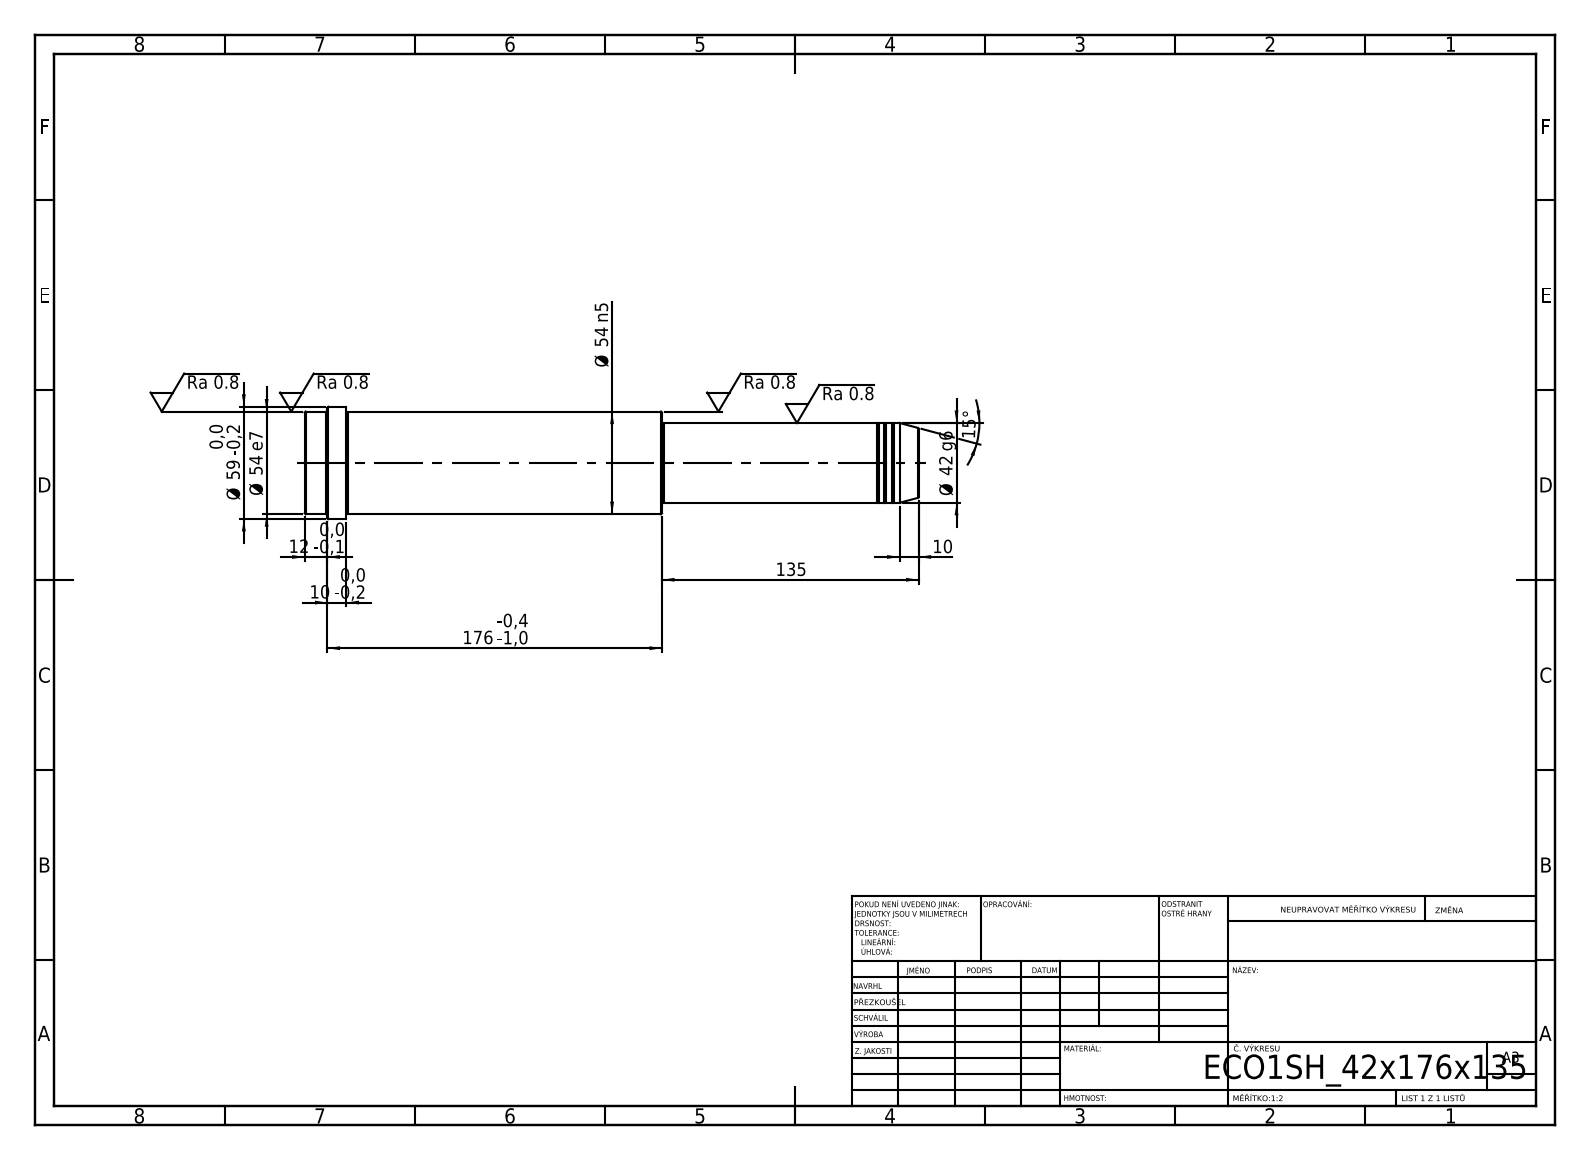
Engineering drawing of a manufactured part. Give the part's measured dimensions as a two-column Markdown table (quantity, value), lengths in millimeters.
| quantity | value |
| --- | --- |
| STEP written by | SolidWorks 2019 (CONFIG_CONTROL_DESIGN) |
| units | millimeters |
| bodies | 1 solid, 52 faces (6 planar, 16 cylindrical, 30 other) |
| overall size | 323 × 59 × 59 |
| volume | 619 922 mm³ |
| surface area | 55 323 mm² |
| round bosses / shafts (diameter × count) | 59 × 1, 54 × 1, 42 × 1, 41 × 1 |
| main face-to-face distances | 323, 135, 188, 301, 166, 22, 311, 176, 10, 12 |
